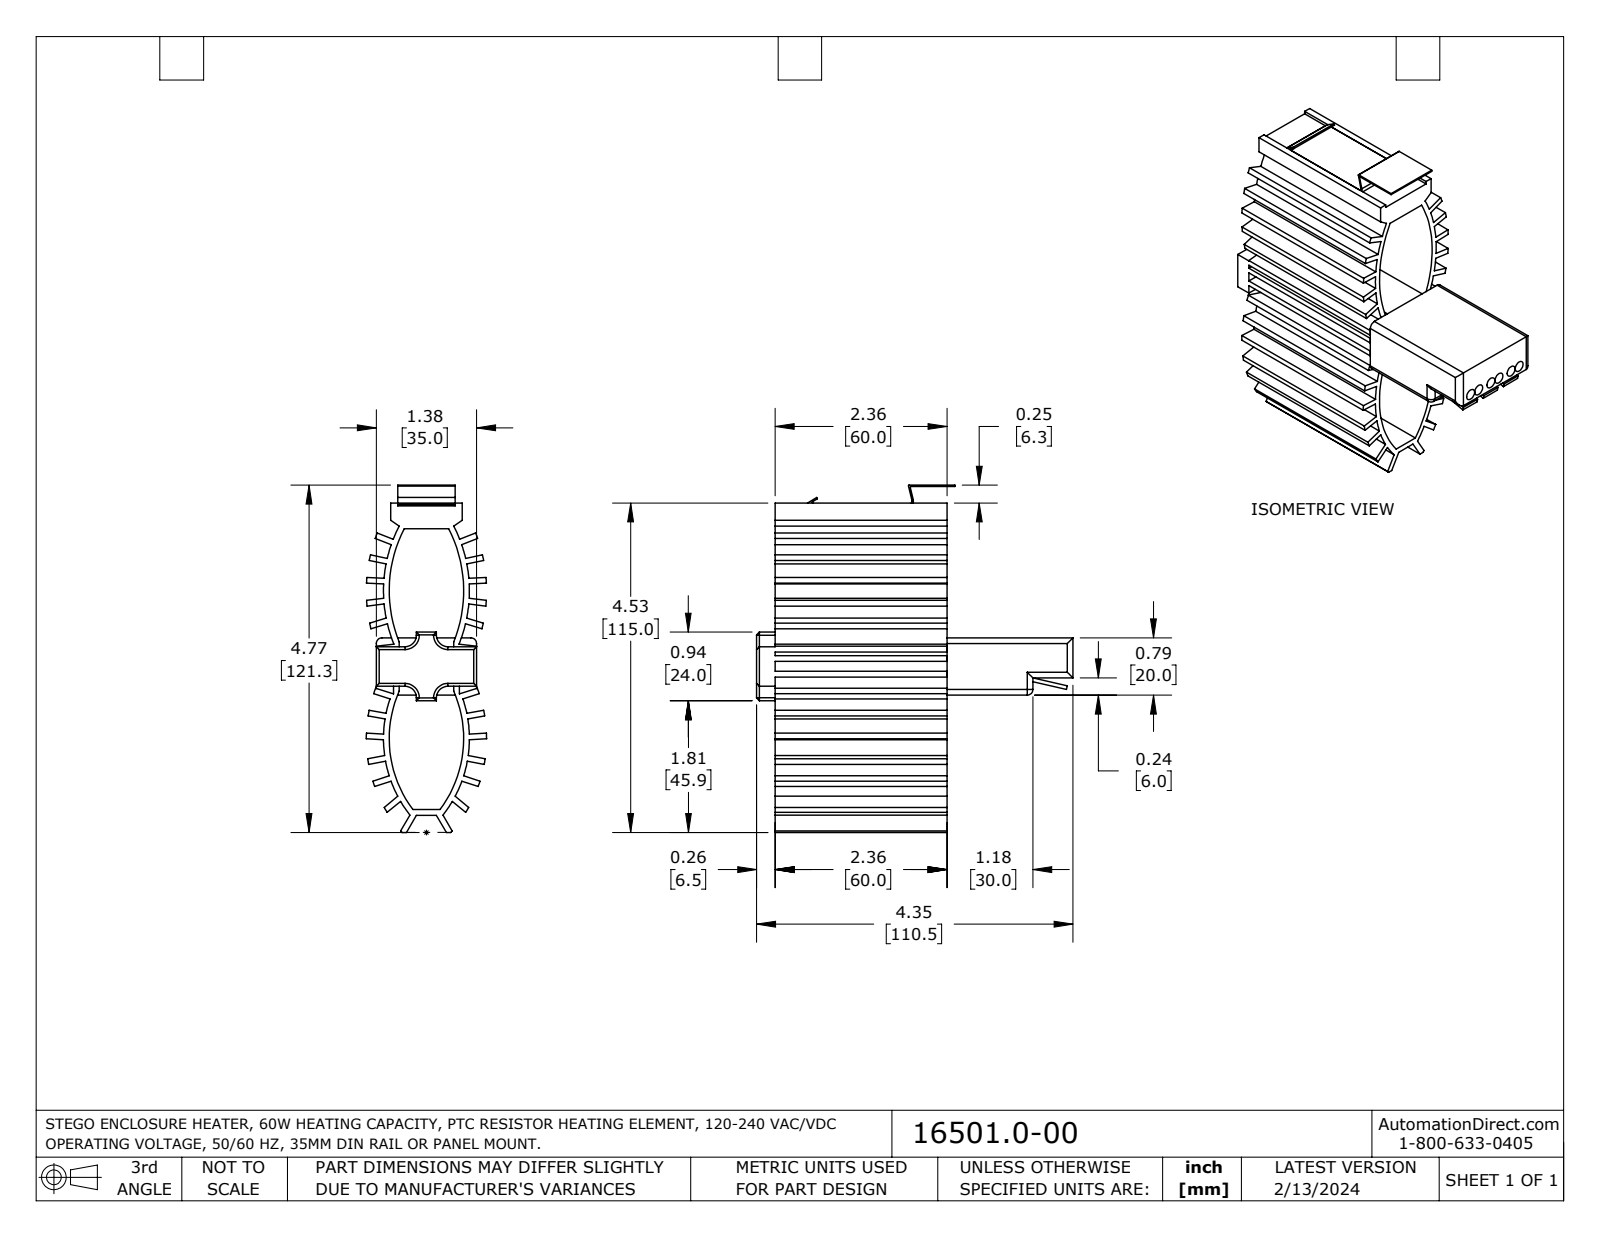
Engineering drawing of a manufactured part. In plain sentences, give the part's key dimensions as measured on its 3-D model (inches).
The part is named "16501.0-00". Its 3-D file was written by "SolidWorks 2023 (AUTOMOTIVE_DESIGN)". It is 3 solids with 244 faces: 160 planar, 78 cylindrical and 6 other. Overall it measures 4.774 by 4.35 by 1.654 inches. Its volume is 5.553 cubic inches and its surface area 100.3 square inches. Round holes: 6 of diameter 0.154. Partial cylindrical surfaces (rounded edges, fillets, slot ends): 11 of radius 0.079, 5 of radius 0.01, 4 of radius 0.157, 2 of radius 1.623, 2 of radius 1.701, 2 of radius 1.863, 2 of radius 1.937, 2 of radius 1.942. The main face-to-face distances are 0.079, 0.315, 0.236, 0.02, 1.063, 0.039, 0.217, 0.827, 1.142, 2.362. The hole center spacings are 0.394, 0.157, 0.236, 0.551, 0.787, 0.63, 0.945.
